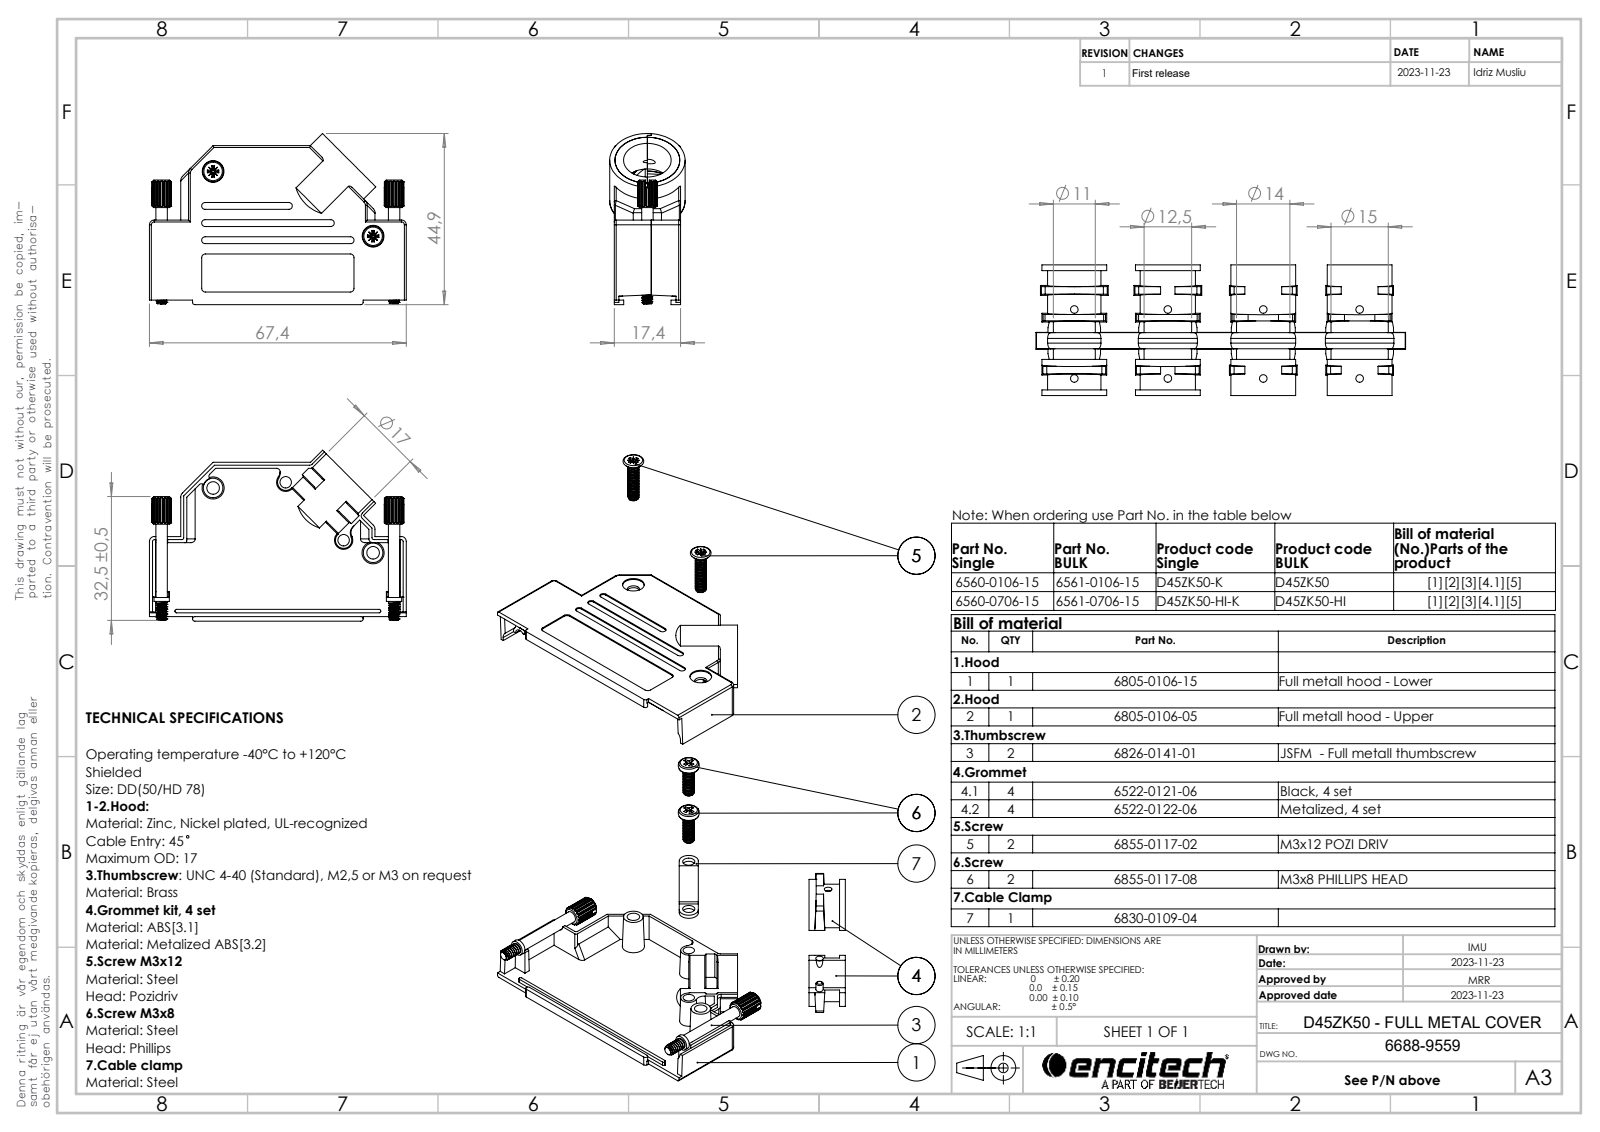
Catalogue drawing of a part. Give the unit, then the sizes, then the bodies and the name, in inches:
Units: inches
Overall size (bounding box): 2.654 × 1.768 × 0.78
Round holes (diameter × count): ⌀0.126 ×4, ⌀0.079 ×3, ⌀0.13 ×2, ⌀0.224 ×2, ⌀0.492 ×1
Round bosses / shafts (diameter × count): ⌀0.118 ×4, ⌀0.157 ×2, ⌀0.114 ×2, ⌀0.112 ×2, ⌀0.075 ×2, ⌀0.78 ×1, ⌀0.669 ×1, ⌀0.571 ×1
Partial cylindrical surfaces — rounded edges, fillets, slot ends (radius × count): R0.02 ×23, R0.039 ×19, R0.004 ×8, R0.059 ×8, R0.035 ×6, R0.012 ×4, R0.016 ×4, R0.024 ×2
Main face-to-face distances: 0.047, 0.638, 0.591, 0.685, 0.035, 0.063, 0.673, 0.626, 0.295, 0.343
Hole centre spacings: 0.278, 0.293, 0.535, 0.742, 0.331, 0.465, 0.559, 0.753
Volume: 0.678 in³ · Surface area: 29.26 in²
Bodies: 11 solids, 988 faces (443 planar, 382 cylindrical, 163 other)
Part name (STEP PRODUCT): 6805-0106-05; 6826-0141-01; 6855-0117-02; 6830-0109-04 (+4 more)
STEP written by: SolidWorks 2021 (AUTOMOTIVE_DESIGN)
